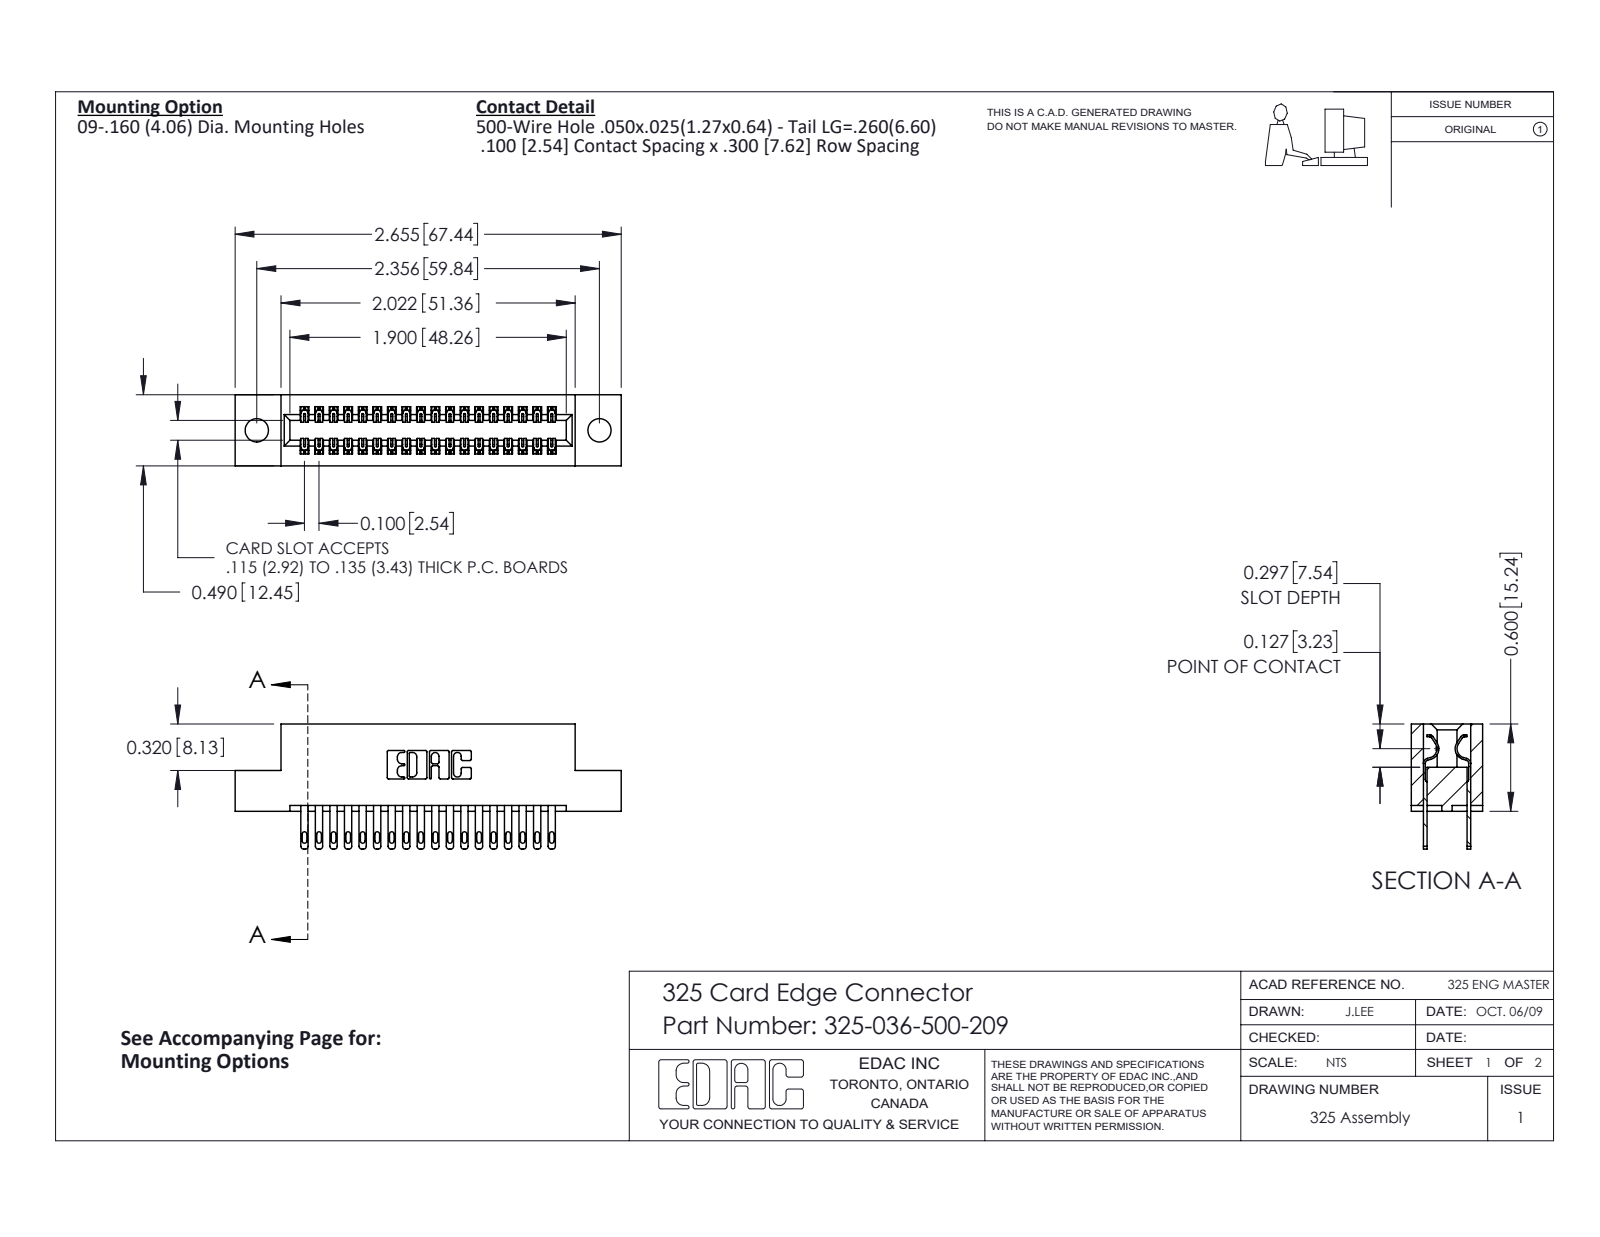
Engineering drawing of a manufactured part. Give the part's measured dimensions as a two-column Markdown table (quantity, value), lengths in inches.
| quantity | value |
| --- | --- |
| part name | 325 Part_.160 TH; 325-292-001_325-293-100; 325-036-500-209 |
| STEP written by | SolidWorks 2016 (CONFIG_CONTROL_DESIGN) |
| units | inches |
| bodies | 37 solids, 1842 faces (1150 planar, 692 cylindrical, 0 other) |
| overall size | 2.655 × 0.86 × 0.49 |
| volume | 0.511 in³ |
| surface area | 15.28 in² |
| round holes (diameter × count) | 0.16 × 2 |
| partial cylindrical surfaces (radius × count) | 0.006 × 54, 0.016 × 36, 0.02 × 36, 0.01 × 22, 0.007 × 6, 0.031 × 6, 0.026 × 3, 0.014 × 2 |
| main face-to-face distances | 0.083, 0.407, 0.3, 0.107, 0.383, 0.025, 0.49, 0.325, 0.6, 0.2 |
| hole center spacings | 2.356 |
